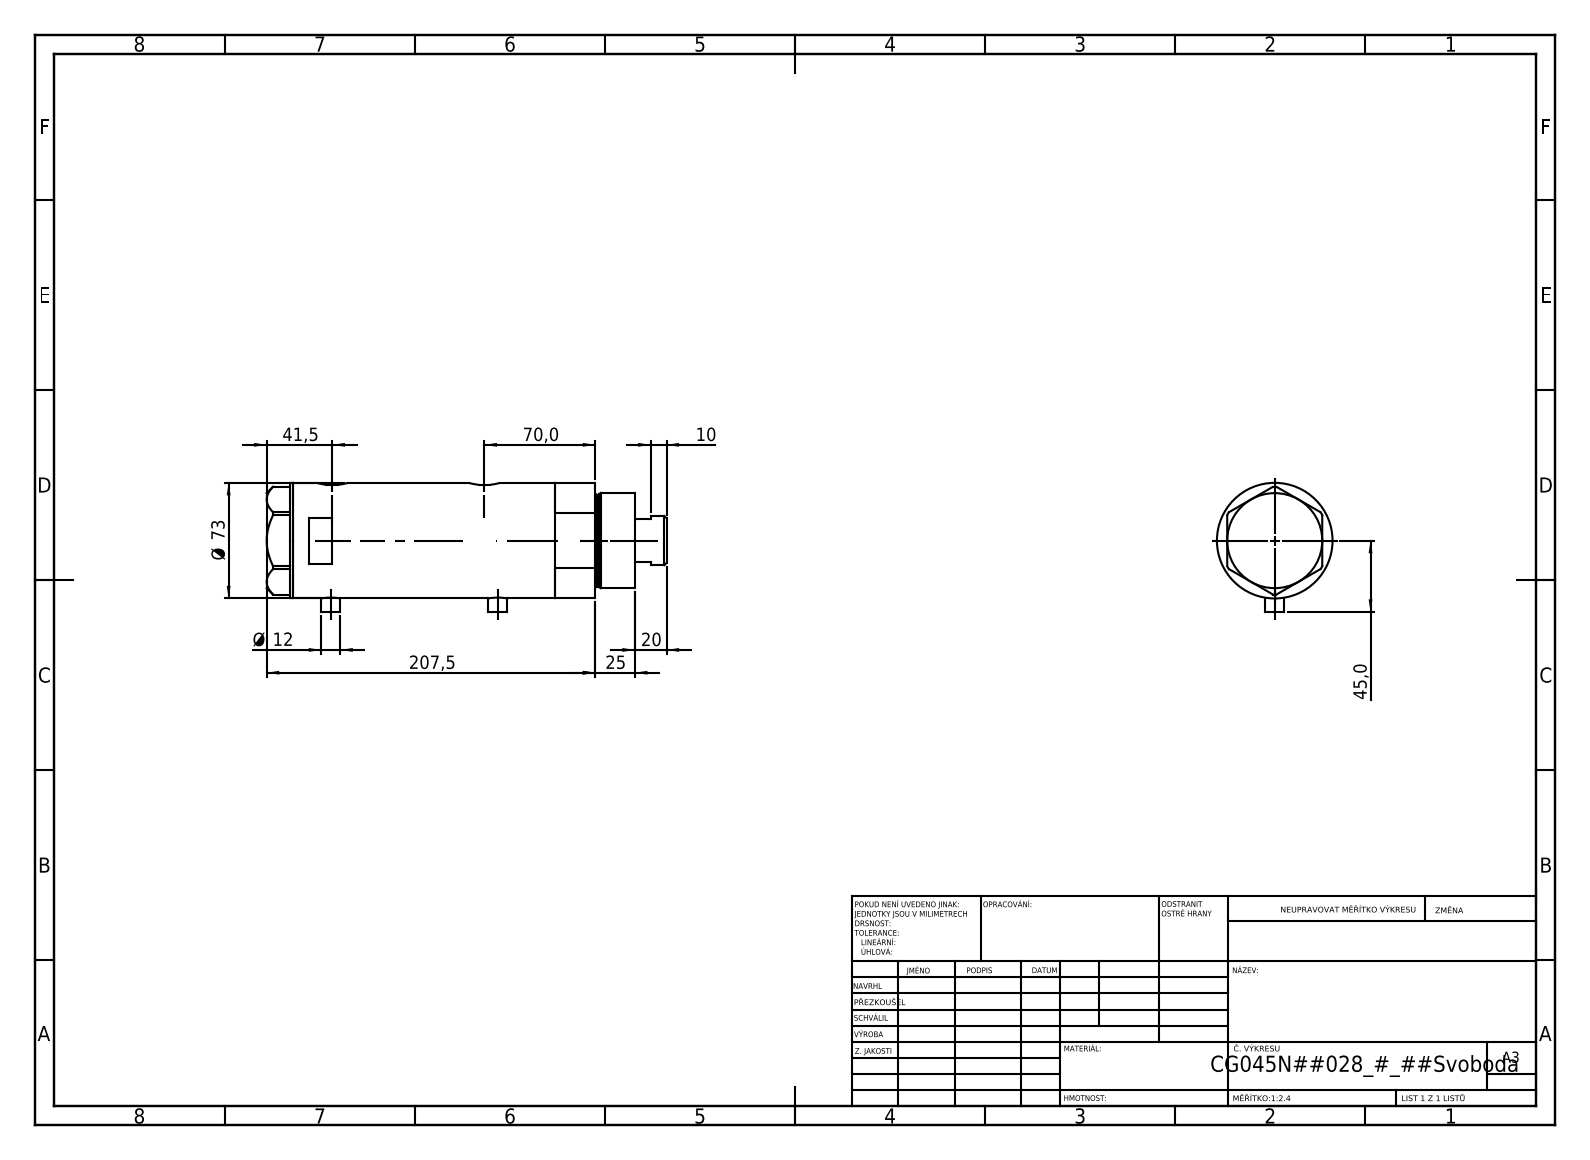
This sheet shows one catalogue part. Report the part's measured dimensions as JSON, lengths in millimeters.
{"part_name": "V270CG_FRONT; V270CG_BACK; V270CG_MIDDLE; V270CG_VC", "step_written_by": "SolidWorks 2019 (CONFIG_CONTROL_DESIGN)", "units": "millimeters", "bodies": {"solids": 4, "faces": 125, "planar": 50, "cylindrical": 55, "other": 20}, "overall_size": [252.5, 81.5, 73], "volume_mm3": 902770, "surface_area_mm2": 150307, "round_holes": [[5, 2], [12.5, 2], [13.16, 2], [10.5, 1], [32, 1], [33.5, 1], [45, 1], [48, 1], [64, 1]], "round_bosses_or_shafts": [[12, 2], [73, 1], [60, 1], [58, 1], [31, 1]], "partial_cylinders_radius": [[10, 2]], "face_to_face_distances": [95, 121, 26, 16.5, 42.5, 137.5, 2, 216, 28, 123], "hole_center_spacings": [1, 8.5, 96, 97, 104.5, 105.5]}
